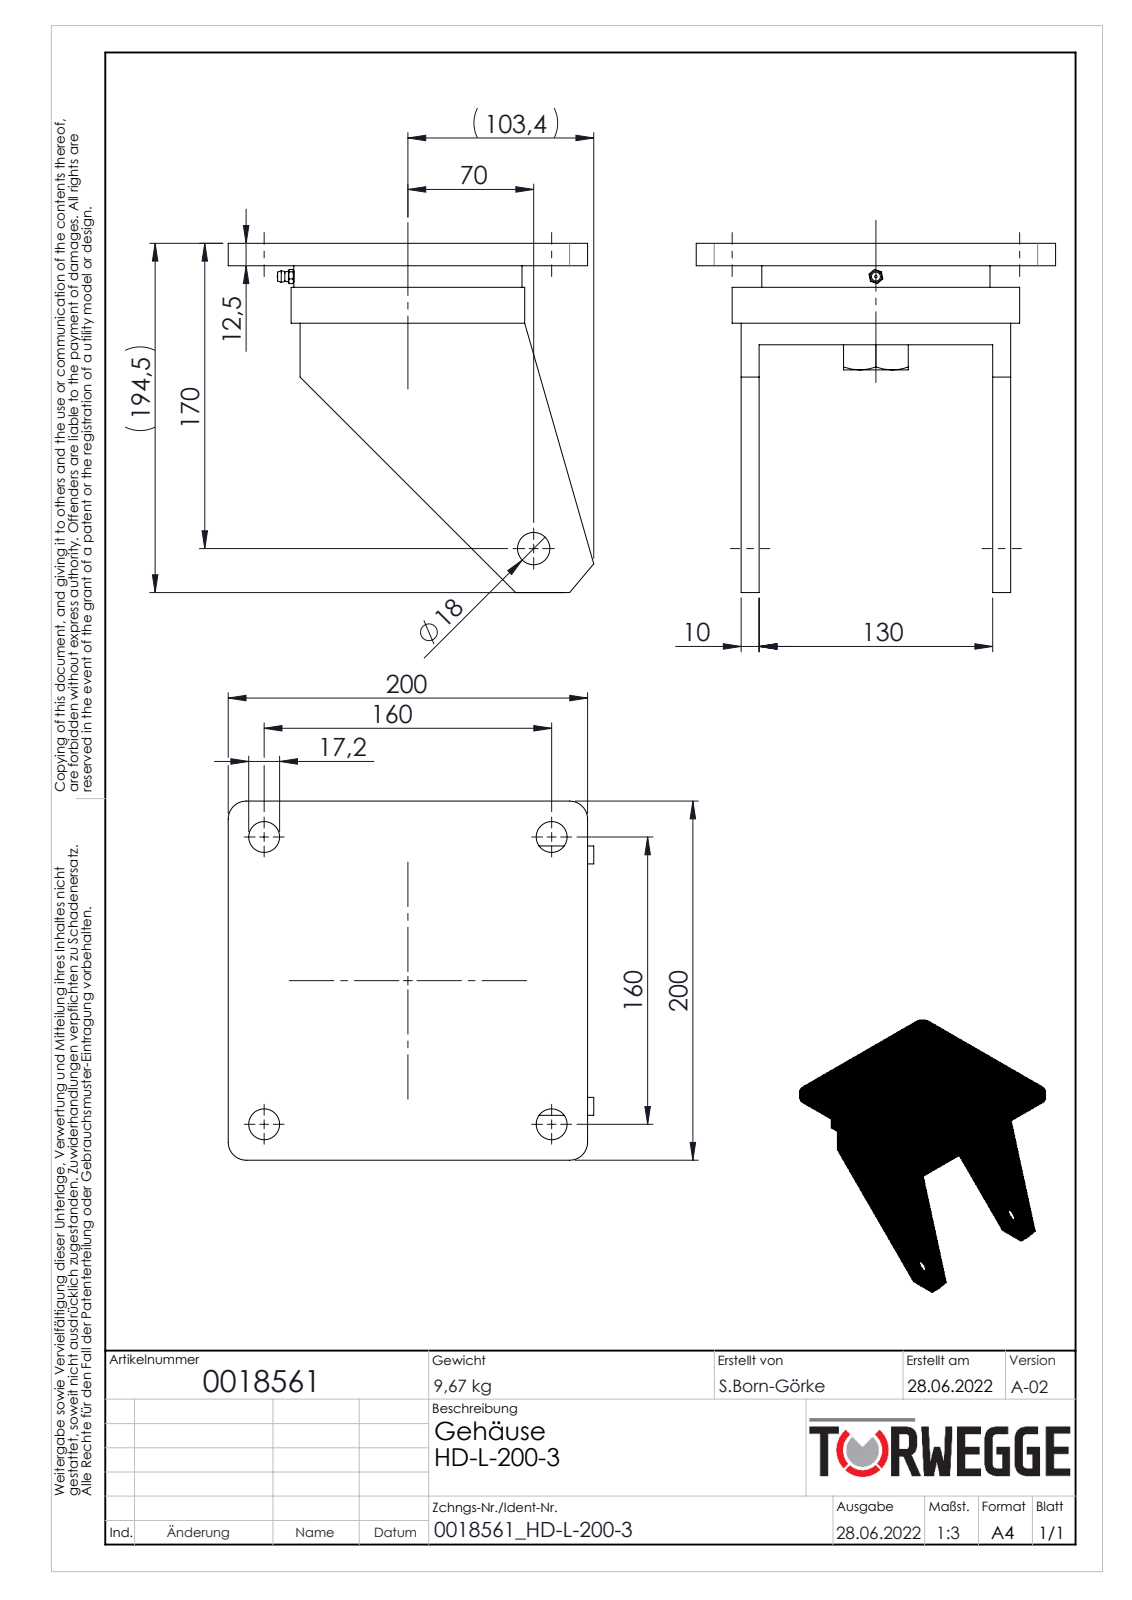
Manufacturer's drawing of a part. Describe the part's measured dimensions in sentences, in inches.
The part is named "0018561". Its 3-D file was written by "SolidWorks 2020 (AUTOMOTIVE_DESIGN)". It is 0 solids with 88 faces: 46 planar, 22 cylindrical and 20 other. Overall it measures 8.009 by 7.874 by 7.657 inches. Round holes: 4 of diameter 0.677, 1 of diameter 0.709, 1 of diameter 0.827. Round bosses or shafts: 1 of diameter 5, 1 of diameter 2.362. Partial cylindrical surfaces (rounded edges, fillets, slot ends): 4 of radius 0.394. The main face-to-face distances are 0.492, 0.394, 5.512, 1.26, 5.118, 5.906, 1.752, 0.472, 0.787, 0.965. The hole center spacings are 4.454, 6.299, 8.908.
